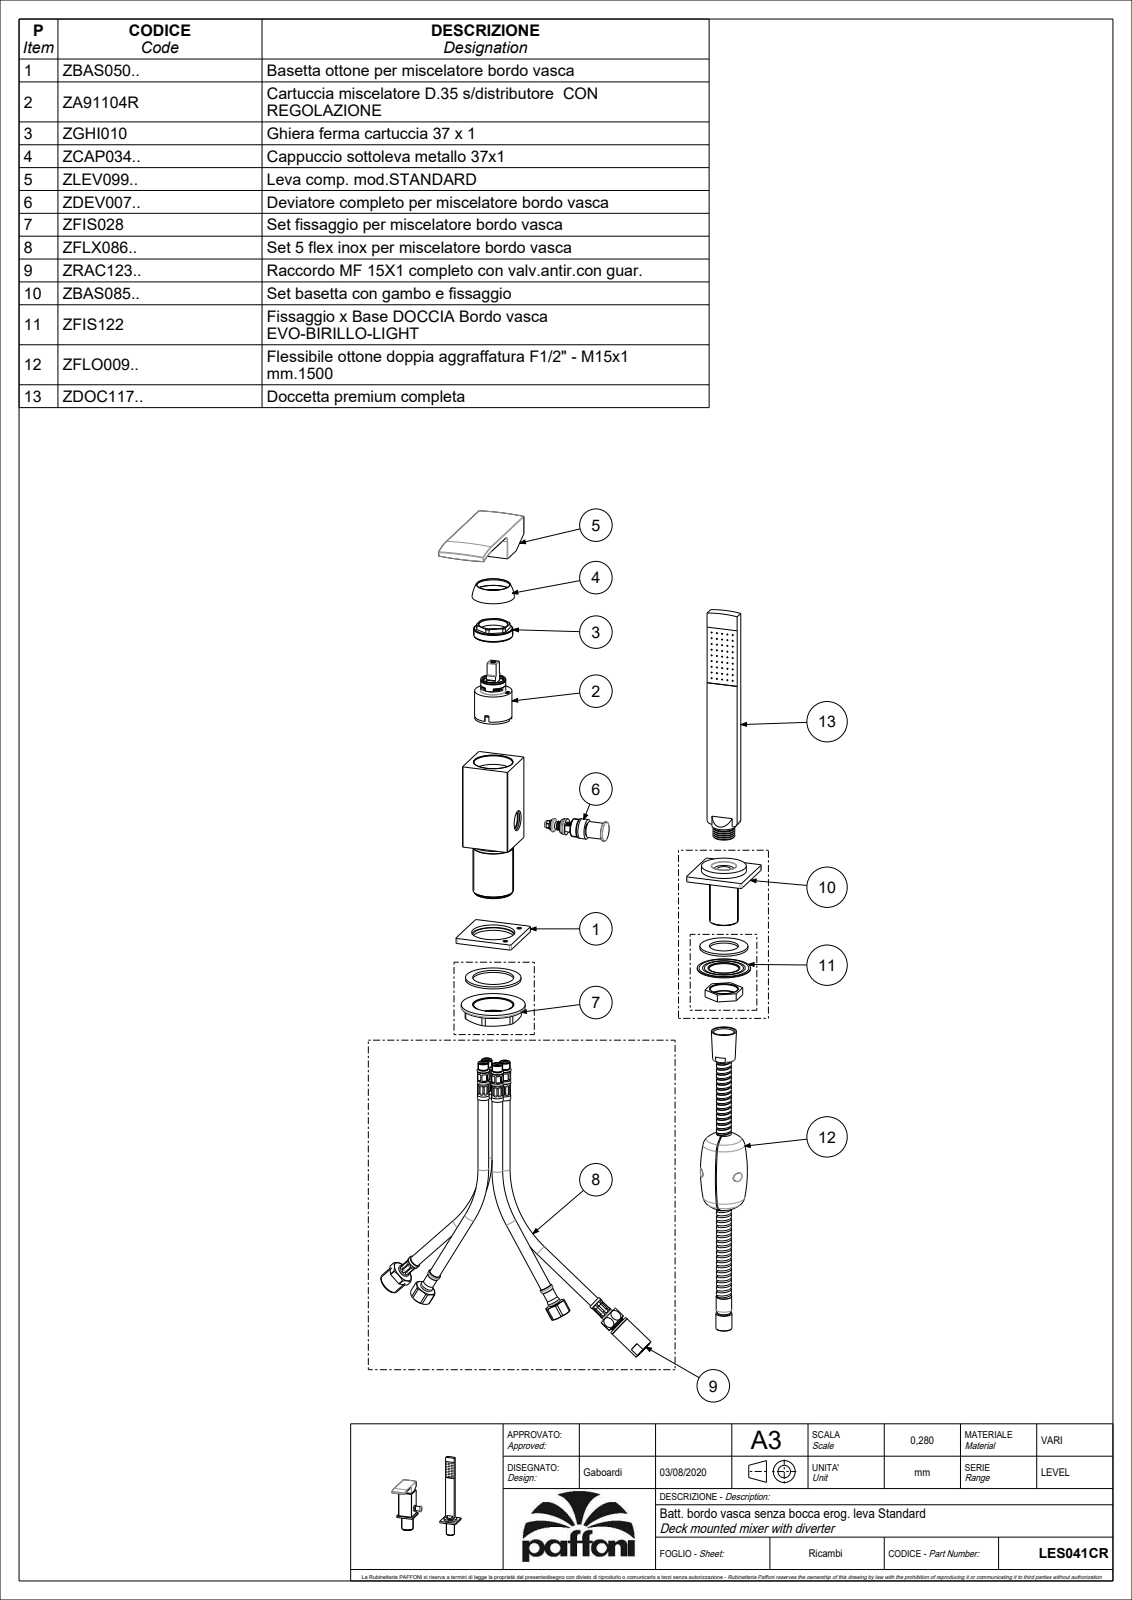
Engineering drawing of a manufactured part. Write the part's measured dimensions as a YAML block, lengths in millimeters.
part_name: "LES041CR"
step_written_by: "CREO PARAMETRIC BY PTC INC, 2020044 (CONFIG_CONTROL_DESIGN)"
units: millimeters
bodies: {solids: 5, faces: 1458, planar: 893, cylindrical: 351, other: 214}
overall_size: [223, 205, 115.88]
volume: 270380
surface_area: 103896
round_holes:
  - {diameter: 7, count: 7}
  - {diameter: 4, count: 2}
  - {diameter: 48, count: 2}
  - {diameter: 3.1, count: 1}
  - {diameter: 3.3, count: 1}
  - {diameter: 4.3, count: 1}
  - {diameter: 4.5, count: 1}
  - {diameter: 5, count: 1}
  - {diameter: 5.5, count: 1}
  - {diameter: 7.2, count: 1}
  - {diameter: 9, count: 1}
  - {diameter: 9.5, count: 1}
round_bosses_or_shafts:
  - {diameter: 2, count: 11}
  - {diameter: 42.5, count: 2}
  - {diameter: 42, count: 1}
  - {diameter: 40, count: 1}
  - {diameter: 38, count: 1}
  - {diameter: 35, count: 1}
  - {diameter: 34.8, count: 1}
  - {diameter: 32.2, count: 1}
partial_cylinders:
  - {radius: 0.5, count: 33}
  - {radius: 1.5, count: 22}
  - {radius: 0.15, count: 11}
  - {radius: 0.3, count: 4}
  - {radius: 2, count: 4}
  - {radius: 1, count: 2}
  - {radius: 4, count: 2}
  - {radius: 300, count: 2}
face_to_face_distances: [45, 27.5, 17.5, 10, 5, 3, 30, 142.5, 157.5, 187.5]
hole_center_spacings: [3, 8.6, 10.63, 14, 14.32, 8, 59.31, 143.09]
